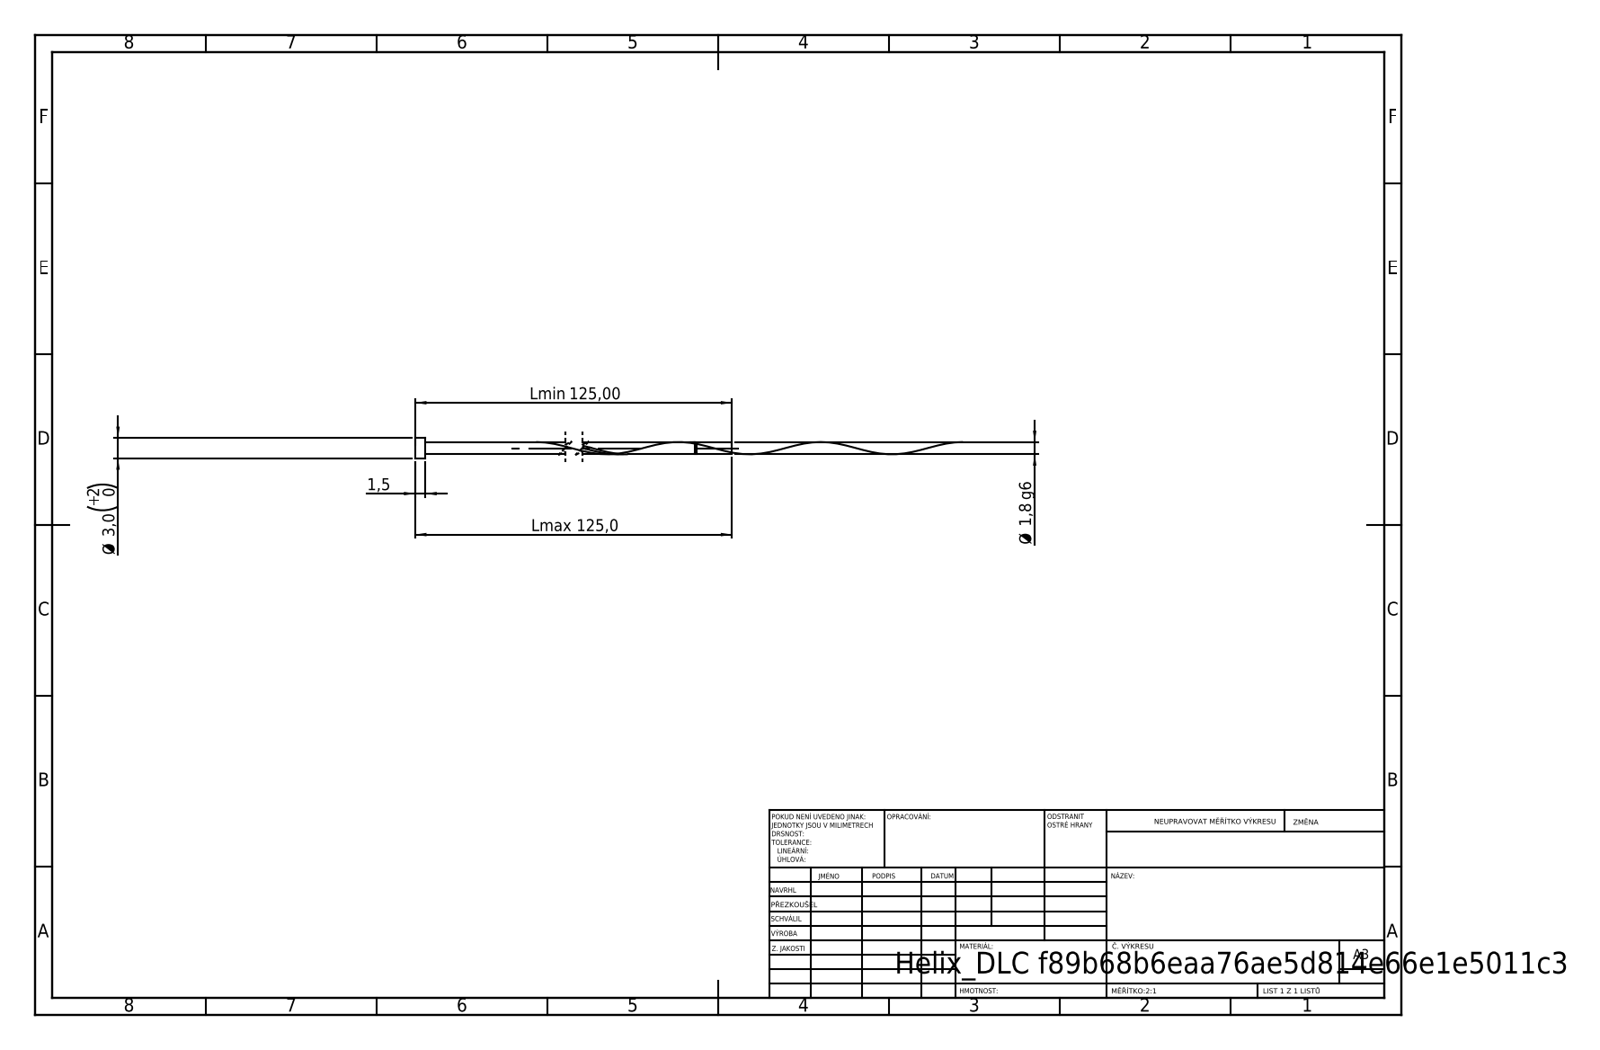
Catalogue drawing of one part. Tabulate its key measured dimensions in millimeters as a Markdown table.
| quantity | value |
| --- | --- |
| STEP written by | SolidWorks 2019 (CONFIG_CONTROL_DESIGN) |
| units | millimeters |
| bodies | 1 solid, 16 faces (6 planar, 9 cylindrical, 1 other) |
| overall size | 125 × 3 × 3 |
| volume | 392 mm³ |
| surface area | 975 mm² |
| round bosses / shafts (diameter × count) | 3 × 1, 1.8 × 1, 1.44 × 1 |
| main face-to-face distances | 1.5, 125, 123.5, 119.86, 118.36, 5.14, 119.5, 118, 0.36, 5.5 |
